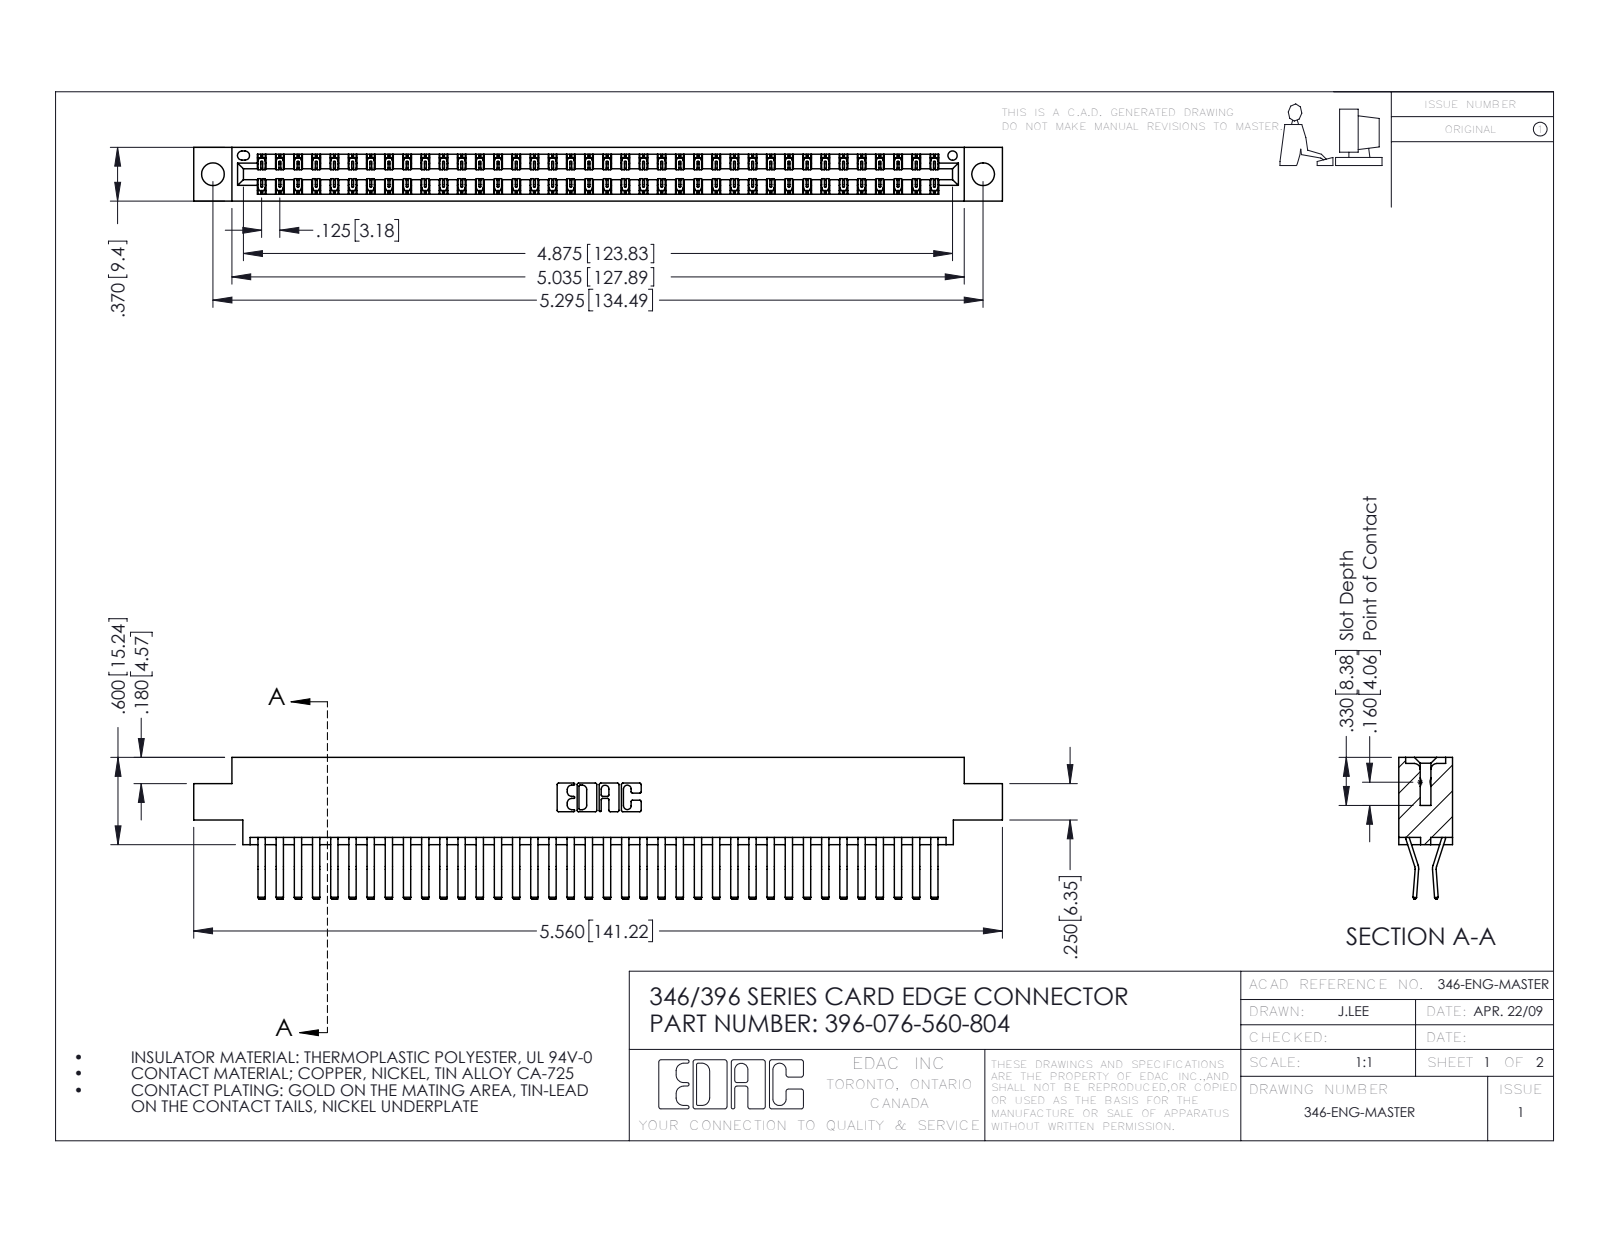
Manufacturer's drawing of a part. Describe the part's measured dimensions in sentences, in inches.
The part is named "345-292-001_560 Tail; 346 Part_0.170 Offset - 0.156 Dia-TH; 396-076-560-804". Its 3-D file was written by "SolidWorks 2016 (CONFIG_CONTROL_DESIGN)". It is 77 solids with 4230 faces: 2740 planar, 1490 cylindrical and 0 other. Overall it measures 5.56 by 0.975 by 0.37 inches. Its volume is 0.854 cubic inches and its surface area 31.77 square inches. Round holes: 2 of diameter 0.156, 1 of diameter 0.064. Partial cylindrical surfaces (rounded edges, fillets, slot ends): 114 of radius 0.006, 22 of radius 0.01, 6 of radius 0.007, 6 of radius 0.031, 3 of radius 0.026, 2 of radius 0.01, 2 of radius 0.014, 2 of radius 0.022. The main face-to-face distances are 0.048, 0.322, 0.37, 0.025, 0.25, 0.072, 0.298, 0.275, 0.148, 0.222. The hole center spacings are 0.246, 5.086, 5.295.
